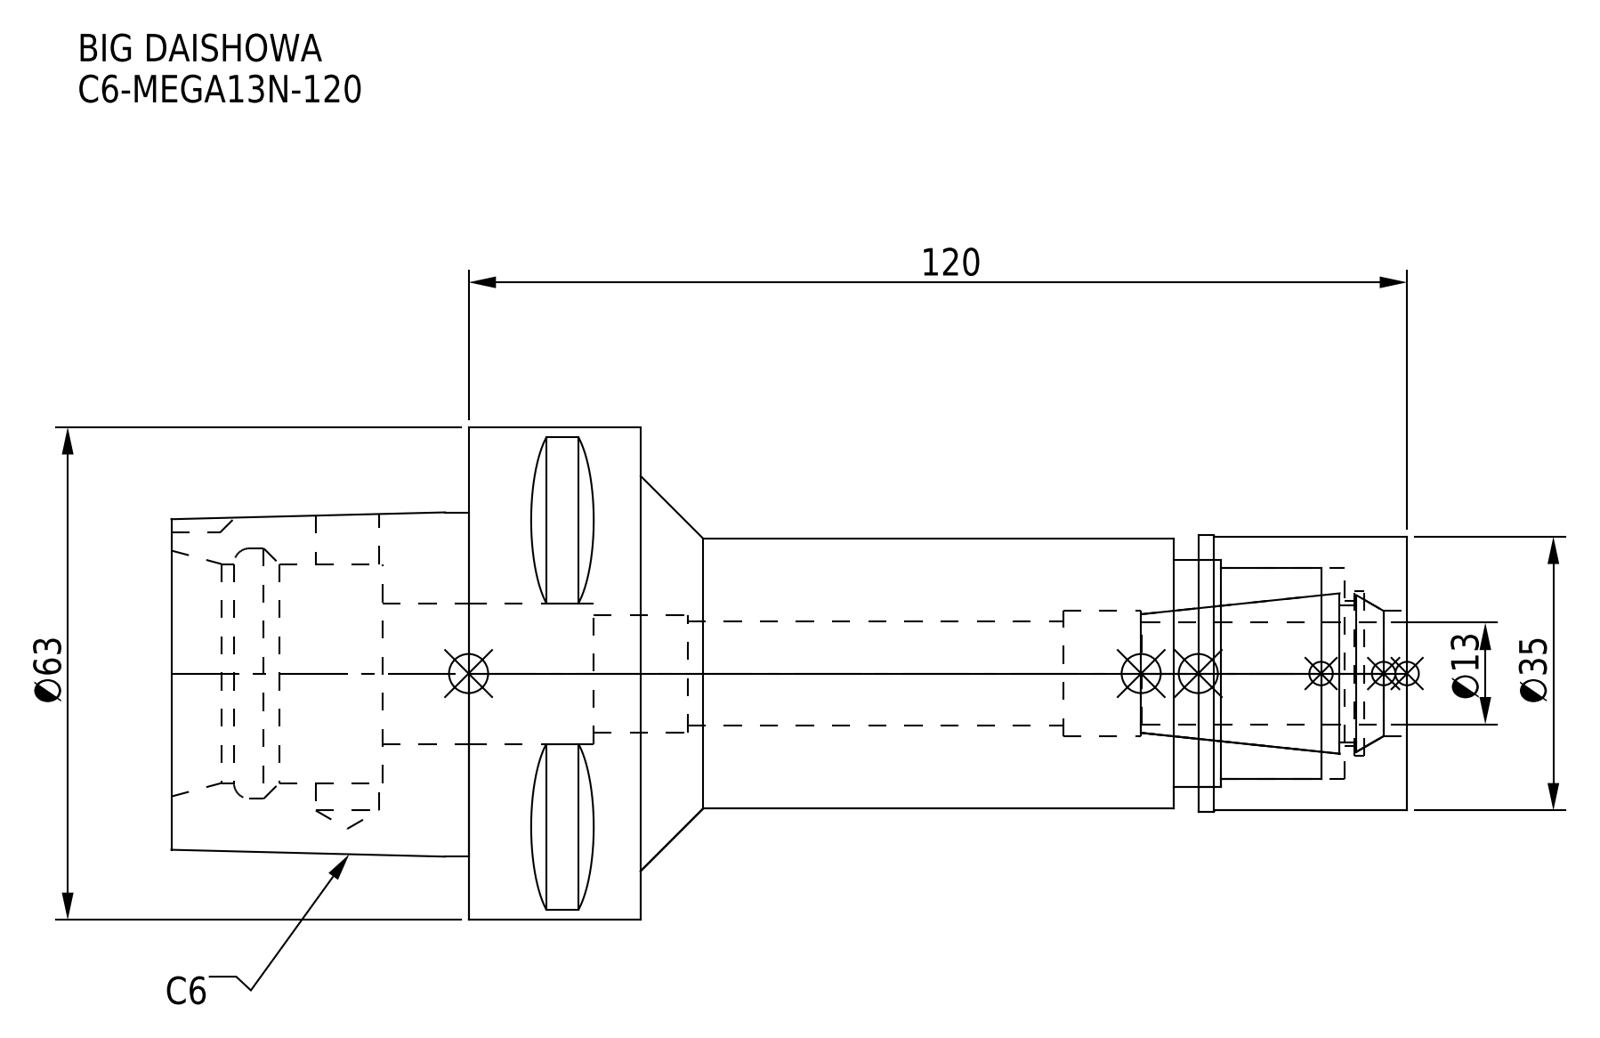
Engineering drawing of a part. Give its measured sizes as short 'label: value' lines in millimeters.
name: DXF_TEMP_ASSY_ASM_4_ASM.stp; MGN13_1.stp; C6-MEGA13N-120_1.stp; C6-MEGA13N-120-130-FreeParts (+3 more)
written by: SolidWorks 2019 (CONFIG_CONTROL_DESIGN)
unit: mm
bodies: 2 solids, 98 faces (39 planar, 41 cylindrical, 18 other)
size: 158 × 63 × 63
volume: 172 008 mm³; area: 39 349 mm²
holes: 1× ⌀8.1, 1× ⌀13.3, 1× ⌀15, 1× ⌀16, 1× ⌀18, 1× ⌀18.5, 1× ⌀21, 1× ⌀27, 1× ⌀28, 1× ⌀29, 1× ⌀32
bosses: 1× ⌀63, 1× ⌀35.3, 1× ⌀35, 1× ⌀34.5
rounds: 1× R5
face distances: 22, 120, 98, 11, 60, 158, 38, 27, 33, 131
